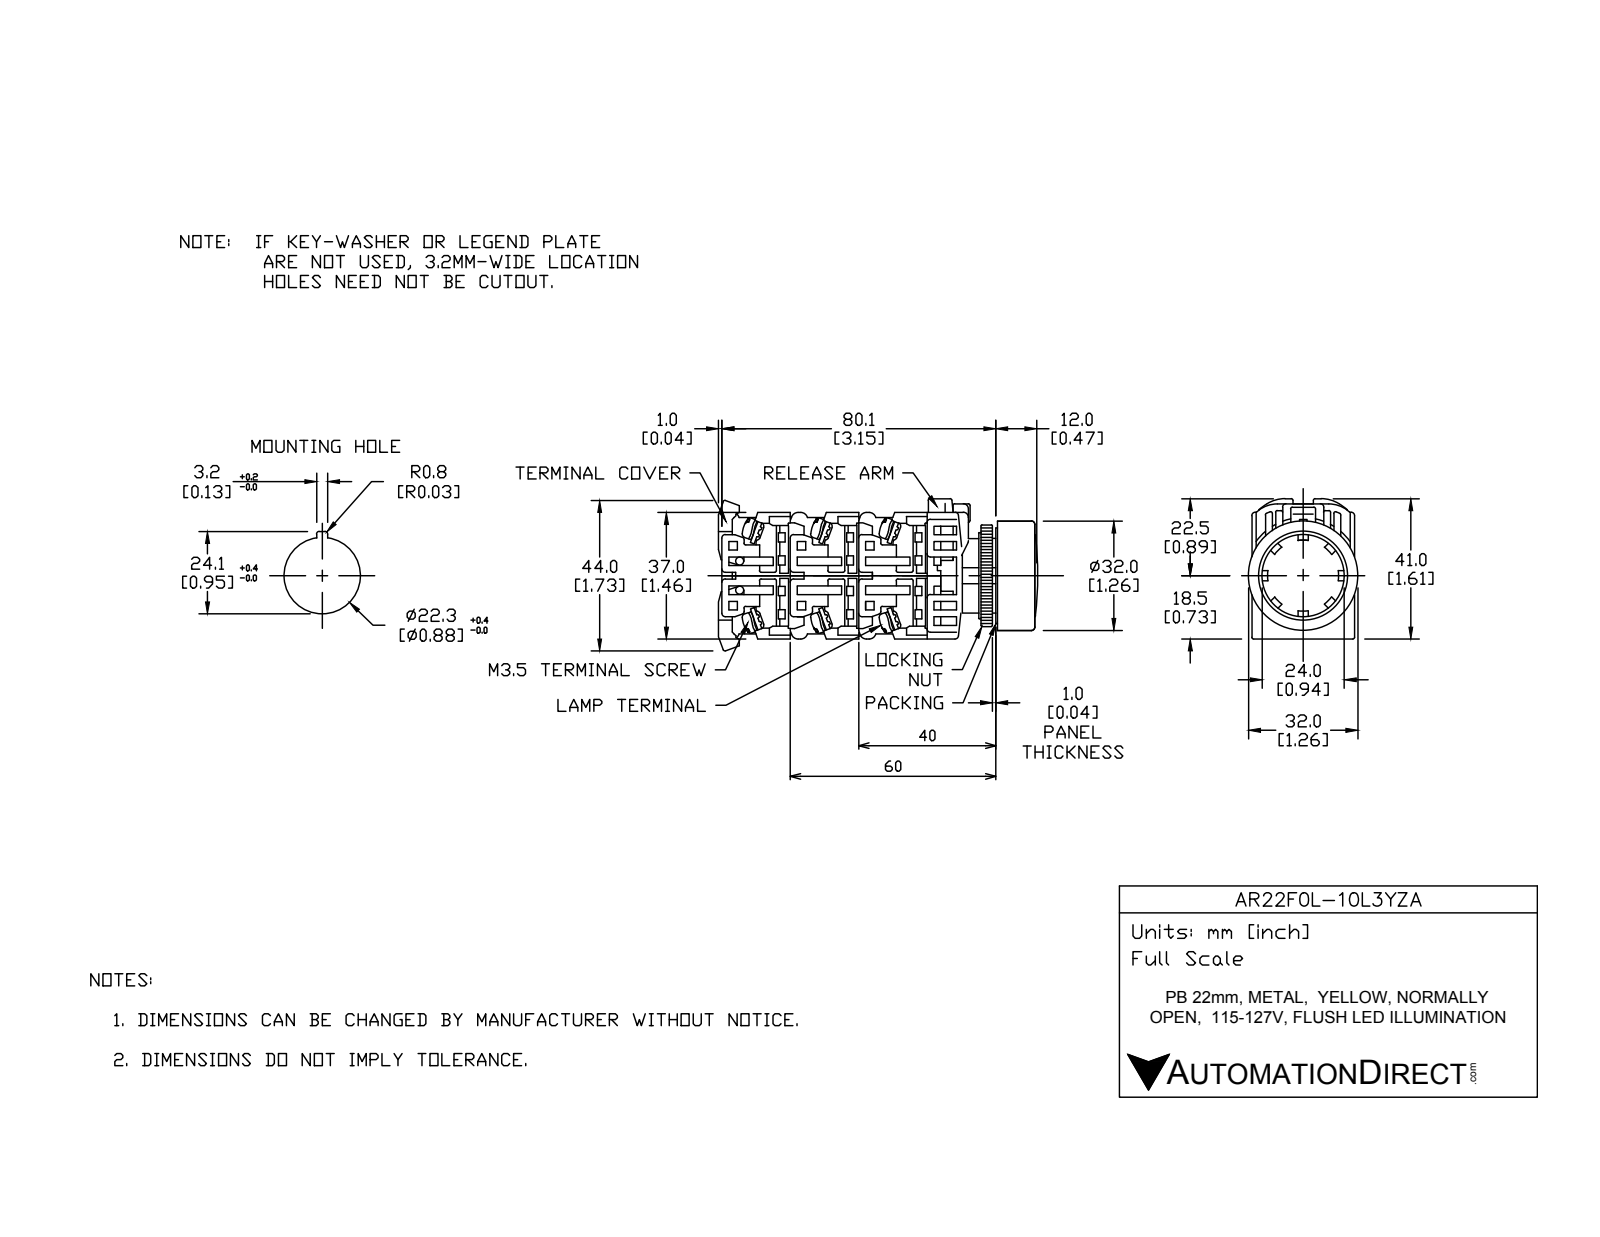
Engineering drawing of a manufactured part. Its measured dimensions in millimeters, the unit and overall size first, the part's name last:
Units: millimetres
Overall size (bounding box): 72.75 × 43.81 × 32
Round holes (diameter × count): ⌀21.8 ×1, ⌀22 ×1, ⌀25 ×1, ⌀31 ×1
Round bosses / shafts (diameter × count): ⌀5 ×4, ⌀32 ×1, ⌀30.5 ×1, ⌀29.8 ×1, ⌀24 ×1, ⌀23.8 ×1, ⌀21.75 ×1, ⌀17 ×1
Partial cylindrical surfaces — rounded edges, fillets, slot ends (radius × count): R0.5 ×32, R1.75 ×8, R5 ×4, R4 ×2, R16.59 ×1, R17.59 ×1
Main face-to-face distances: 1, 18, 29, 20, 28.5, 3, 2, 21, 0.35, 7.5
Volume: 47 521 mm³ · Surface area: 25 721 mm²
Bodies: 16 solids, 451 faces (317 planar, 99 cylindrical, 35 other)
Part name (STEP PRODUCT): AR22F0L-10L3YZA
STEP written by: SolidWorks 2017 (AUTOMOTIVE_DESIGN)
